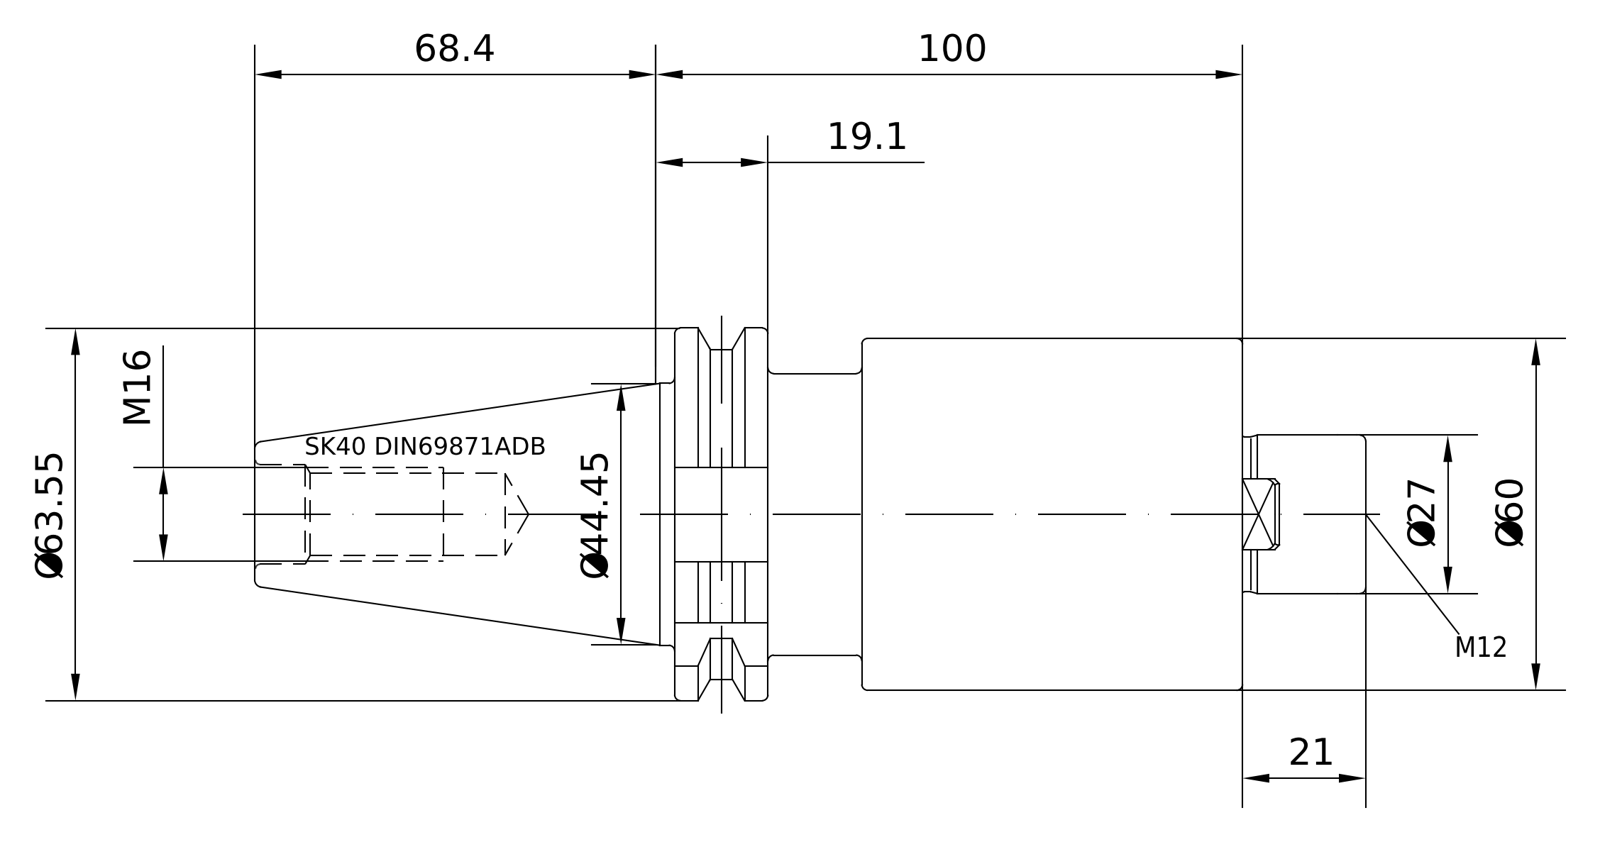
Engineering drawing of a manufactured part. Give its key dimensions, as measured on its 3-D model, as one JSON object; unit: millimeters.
{"part_name": "40-351-27", "step_written_by": "PRO/ENGINEER BY PARAMETRIC TECHNOLOGY CORPORATION, 2010430 (CONFIG_CONTROL_DESIGN)", "units": "millimeters", "bodies": {"solids": 1, "faces": 119, "planar": 34, "cylindrical": 33, "other": 52}, "overall_size": [189.25, 63.52, 61.42], "volume_mm3": 328496, "surface_area_mm2": 40751, "round_holes": [[10.2, 1], [12, 1], [13.84, 1], [17.01, 1], [17.5, 1]], "round_bosses_or_shafts": [[60, 1], [48, 1], [43.75, 1], [27, 1], [16.01, 1]], "partial_cylinders_radius": [[1.35, 5], [28, 1], [31.76, 1]], "face_to_face_distances": [96.8, 15.85, 80.95, 31.85, 16, 64.95, 117.8, 101.95, 85.95, 21]}
